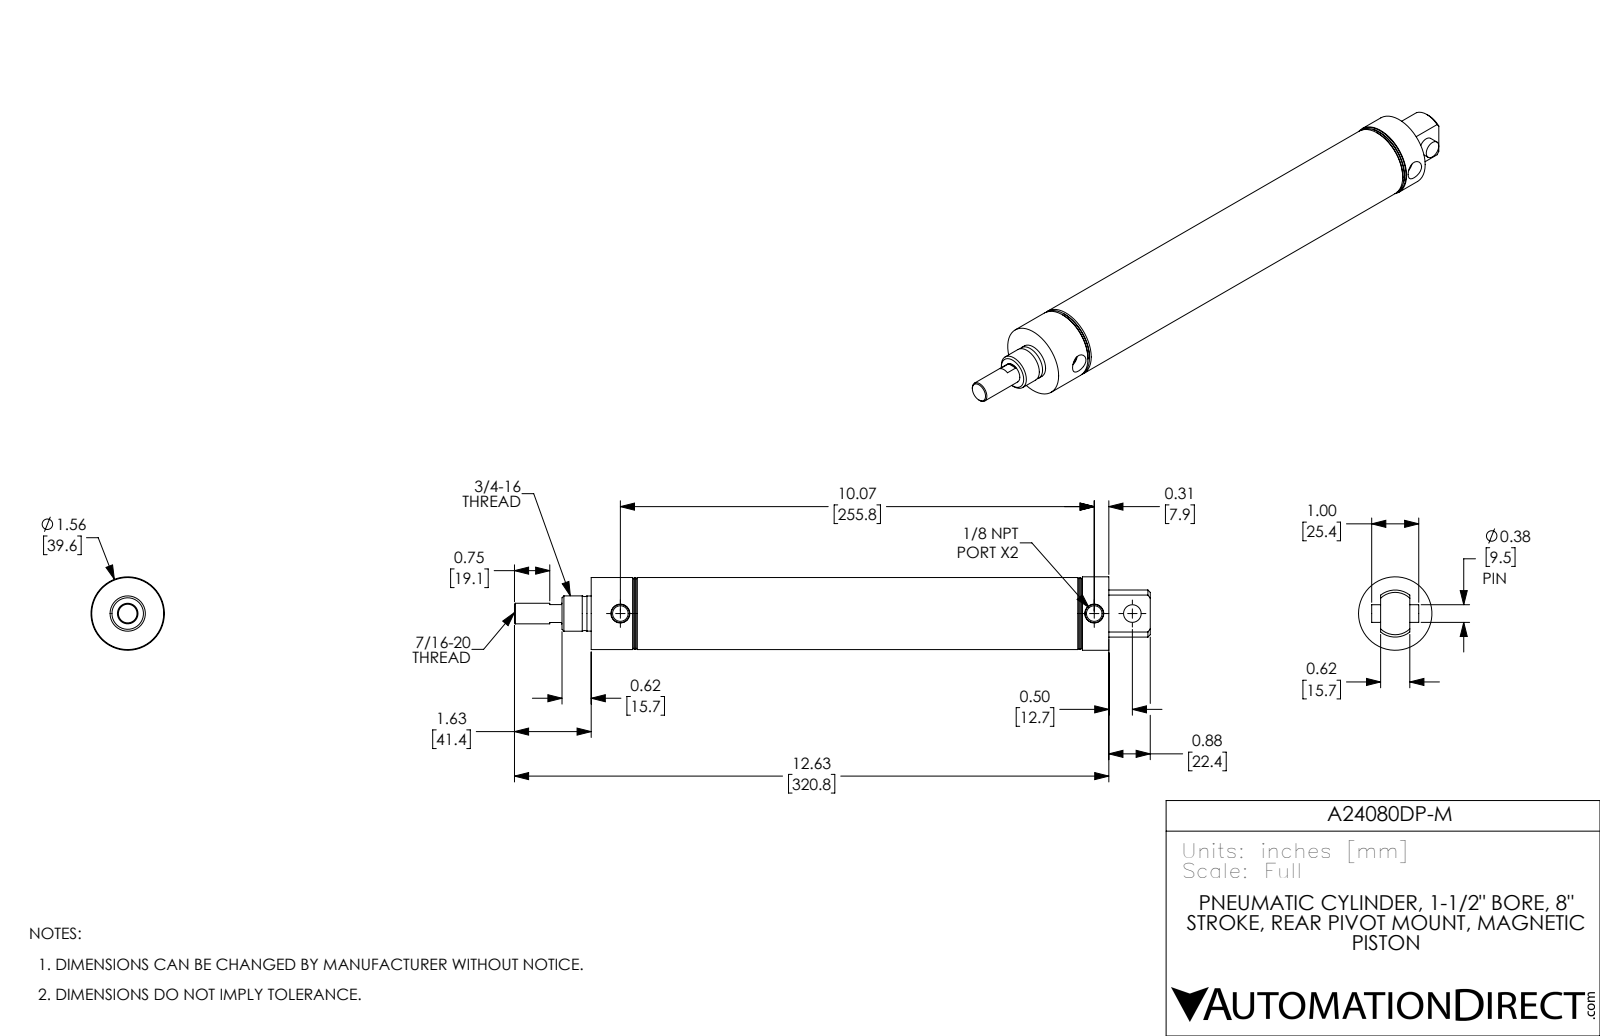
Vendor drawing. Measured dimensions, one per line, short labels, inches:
name: A24080DP-M-MainBody; A24080DP-M; A24080DP-M-Pin; A24080DP-M-Rod
written by: SolidWorks 2017 (AUTOMOTIVE_DESIGN)
unit: in
bodies: 3 solids, 84 faces (22 planar, 28 cylindrical, 34 other)
size: 13.51 × 1.56 × 1.56
volume: 8.18 in³; area: 130.6 in²
holes: 2× ⌀0.332, 1× ⌀0.375, 1× ⌀0.437, 1× ⌀1.5
bosses: 1× ⌀1.56, 1× ⌀1.53, 1× ⌀0.75, 1× ⌀0.746
rounds: 1× R0.5
face distances: 1.25, 9.75, 8.5, 0.5, 8, 9.25, 1.75, 11, 0.62, 0.88
hole spacings: 0.81, 10.07, 10.88
